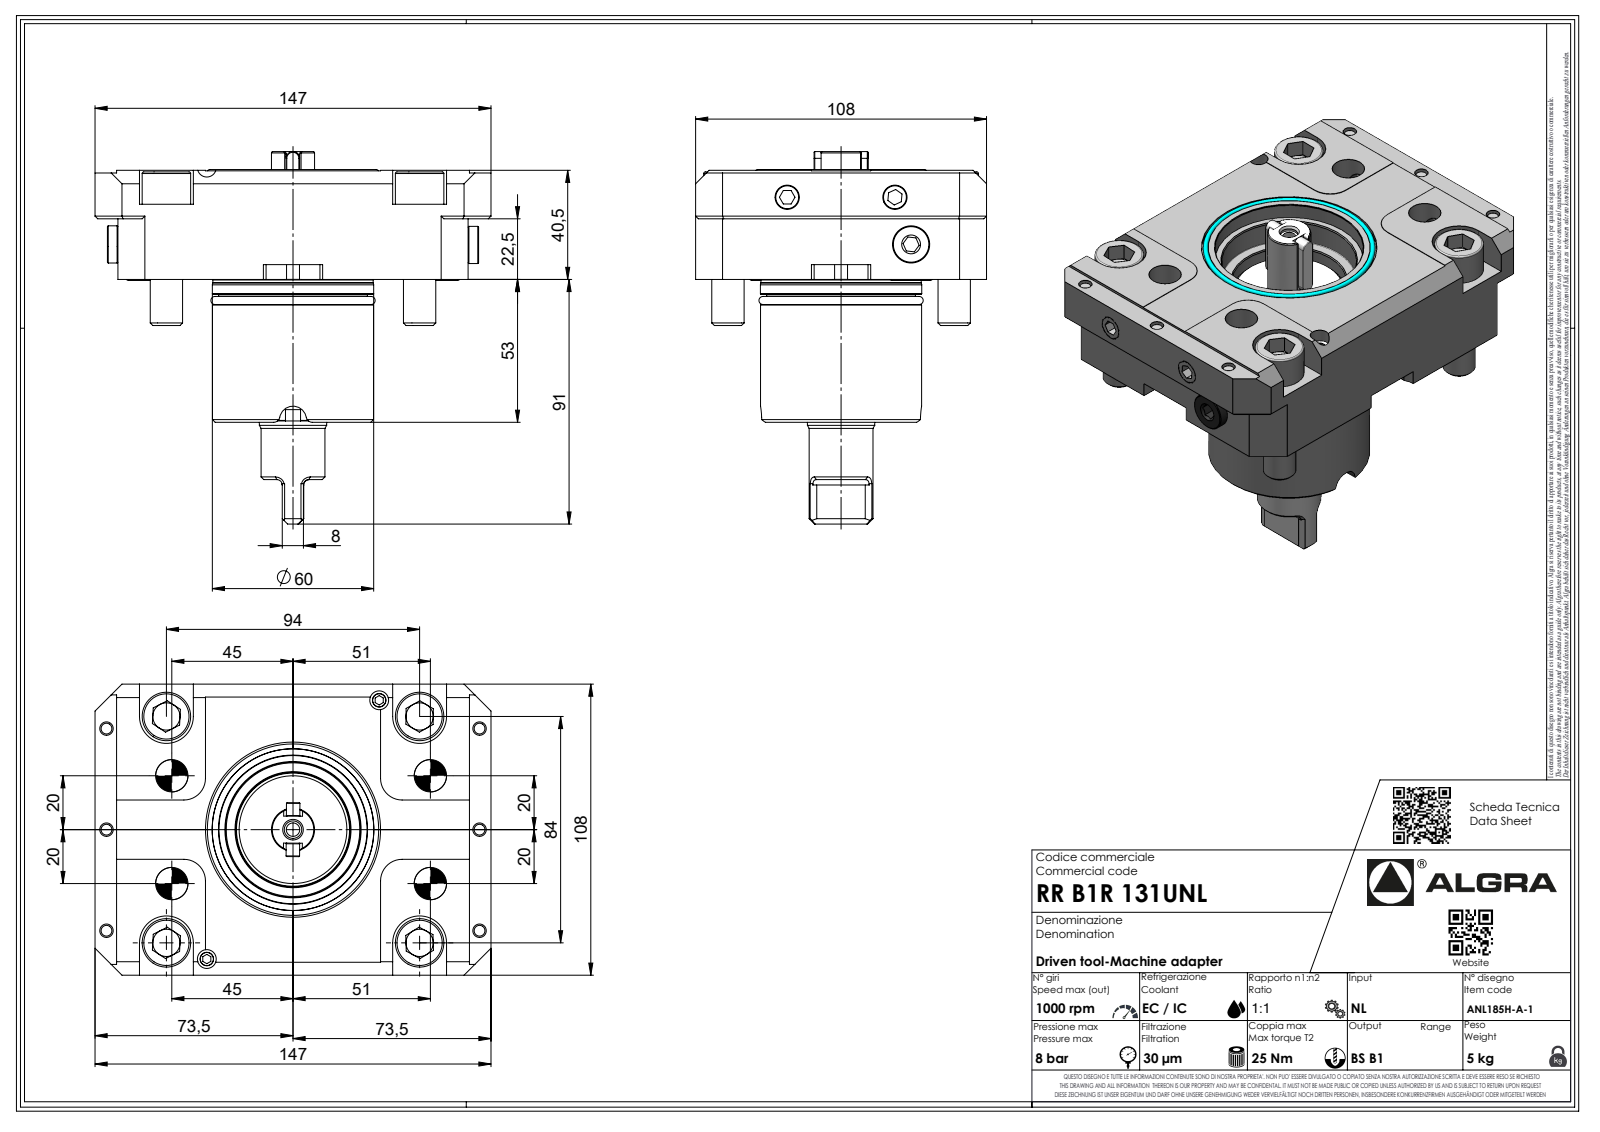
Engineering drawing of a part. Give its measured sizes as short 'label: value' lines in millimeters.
name: RRB1R131UNL
written by: SolidWorks 2023 (AUTOMOTIVE_DESIGN)
unit: mm
bodies: 1 solid, 497 faces (326 planar, 88 cylindrical, 83 other)
size: 147 × 138.2 × 108
volume: 734 572 mm³; area: 71 310 mm²
holes: 1× ⌀2.1
bosses: 4× ⌀18, 4× ⌀12, 1× ⌀59.9, 1× ⌀59.8, 1× ⌀59.5, 1× ⌀55.2, 1× ⌀25, 1× ⌀23.7
rounds: 21× R8, 8× R0.25, 7× R0.33, 7× R0.52, 7× R3.7, 4× R10, 2× R1, 2× R2
face distances: 40.3, 40.5, 108, 17, 8.5, 138.5, 5.5, 34.8, 35, 130
